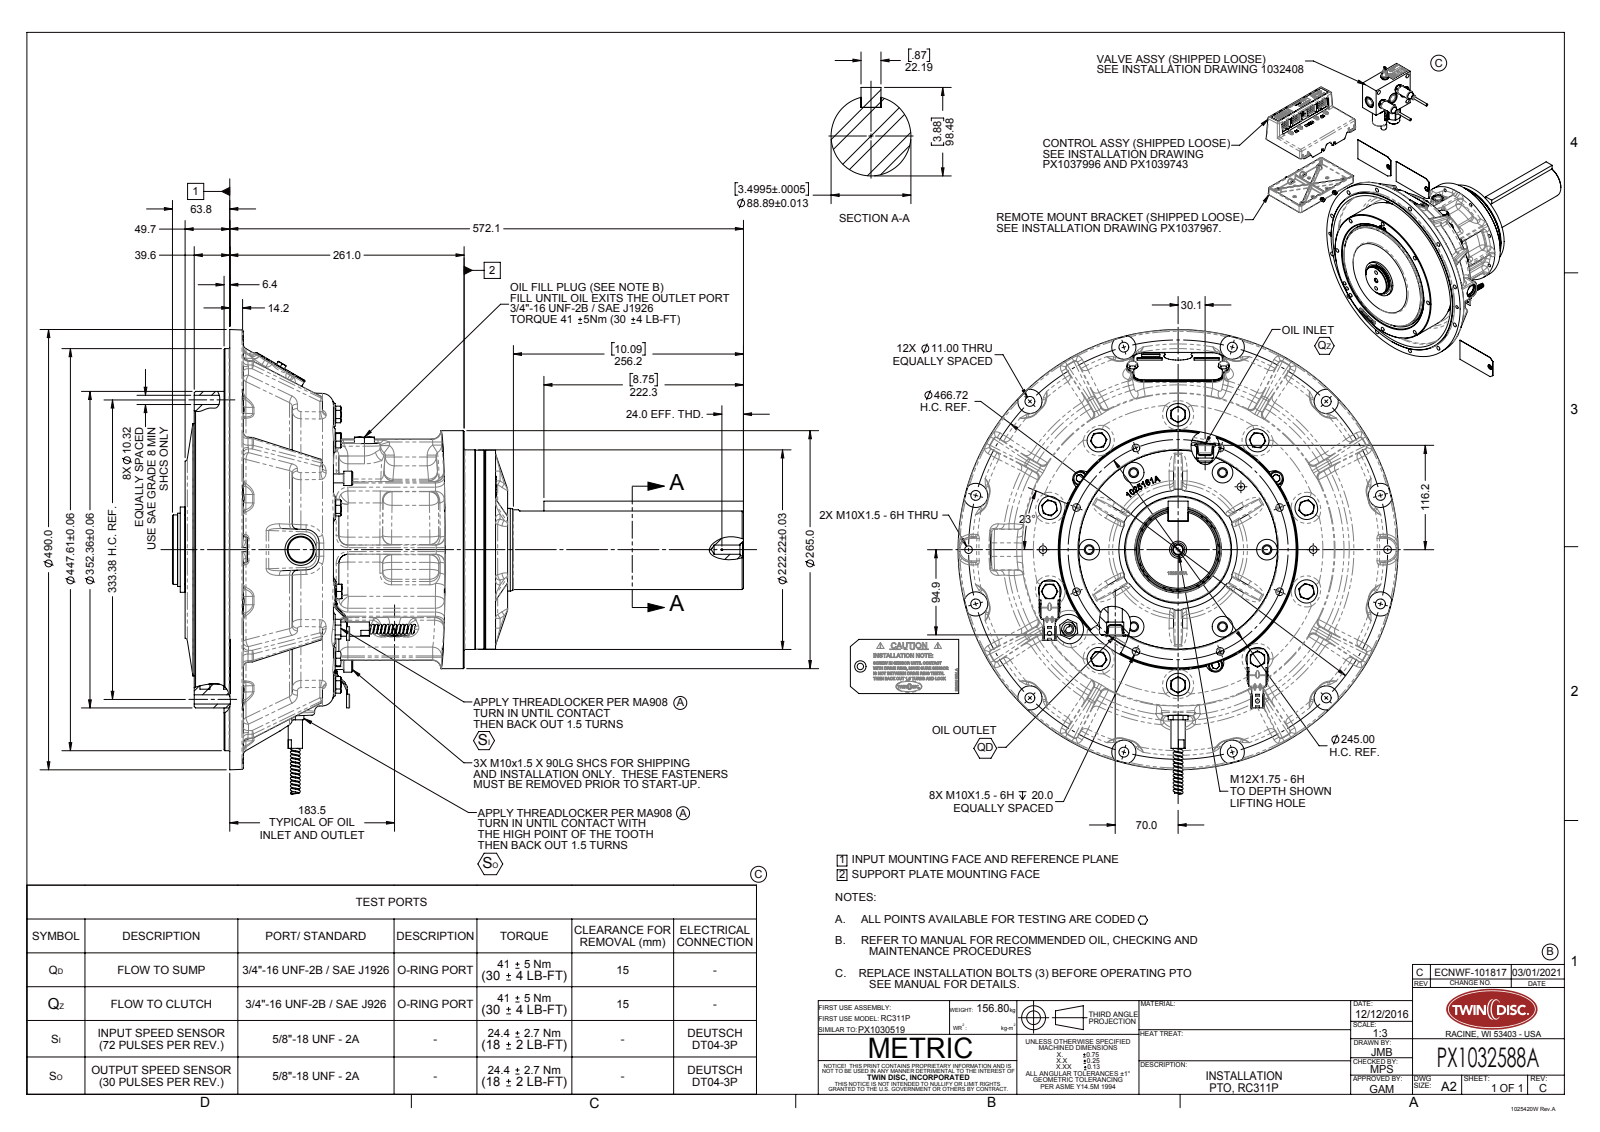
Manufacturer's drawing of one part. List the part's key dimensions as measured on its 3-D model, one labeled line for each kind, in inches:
Part name (STEP PRODUCT): PX1032588A
STEP written by: SolidWorks 2019 (AUTOMOTIVE_DESIGN)
Units: inches
Bodies: 0 solids, 2016 faces (554 planar, 468 cylindrical, 994 other)
Overall size (bounding box): 25.038 × 20.376 × 19.293
Round holes (diameter × count): ⌀0.335 ×14, ⌀0.433 ×12, ⌀1.06 ×12, ⌀0.406 ×8, ⌀0.906 ×5, ⌀0.402 ×3, ⌀1.188 ×3, ⌀0.187 ×2, ⌀0.375 ×2, ⌀0.75 ×2, ⌀0.425 ×1, ⌀1 ×1
Round bosses / shafts (diameter × count): ⌀0.63 ×3, ⌀0.394 ×3, ⌀0.315 ×2, ⌀17.622 ×1, ⌀13.873 ×1, ⌀12.756 ×1, ⌀11.063 ×1, ⌀10.433 ×1
Partial cylindrical surfaces — rounded edges, fillets, slot ends (radius × count): R0.118 ×103, R0.394 ×39, R0.392 ×32, R0.236 ×27, R0.059 ×17, R0.197 ×12, R0.06 ×8, R0.5 ×6
Main face-to-face distances: 1.307, 1.955, 0.648, 4.134, 5.441, 6.089, 5.693, 1.559, 0.252, 0.396
Hole centre spacings: 9.187, 12.993, 17.749, 9.004, 10.869, 12.257, 3.898, 4.756
